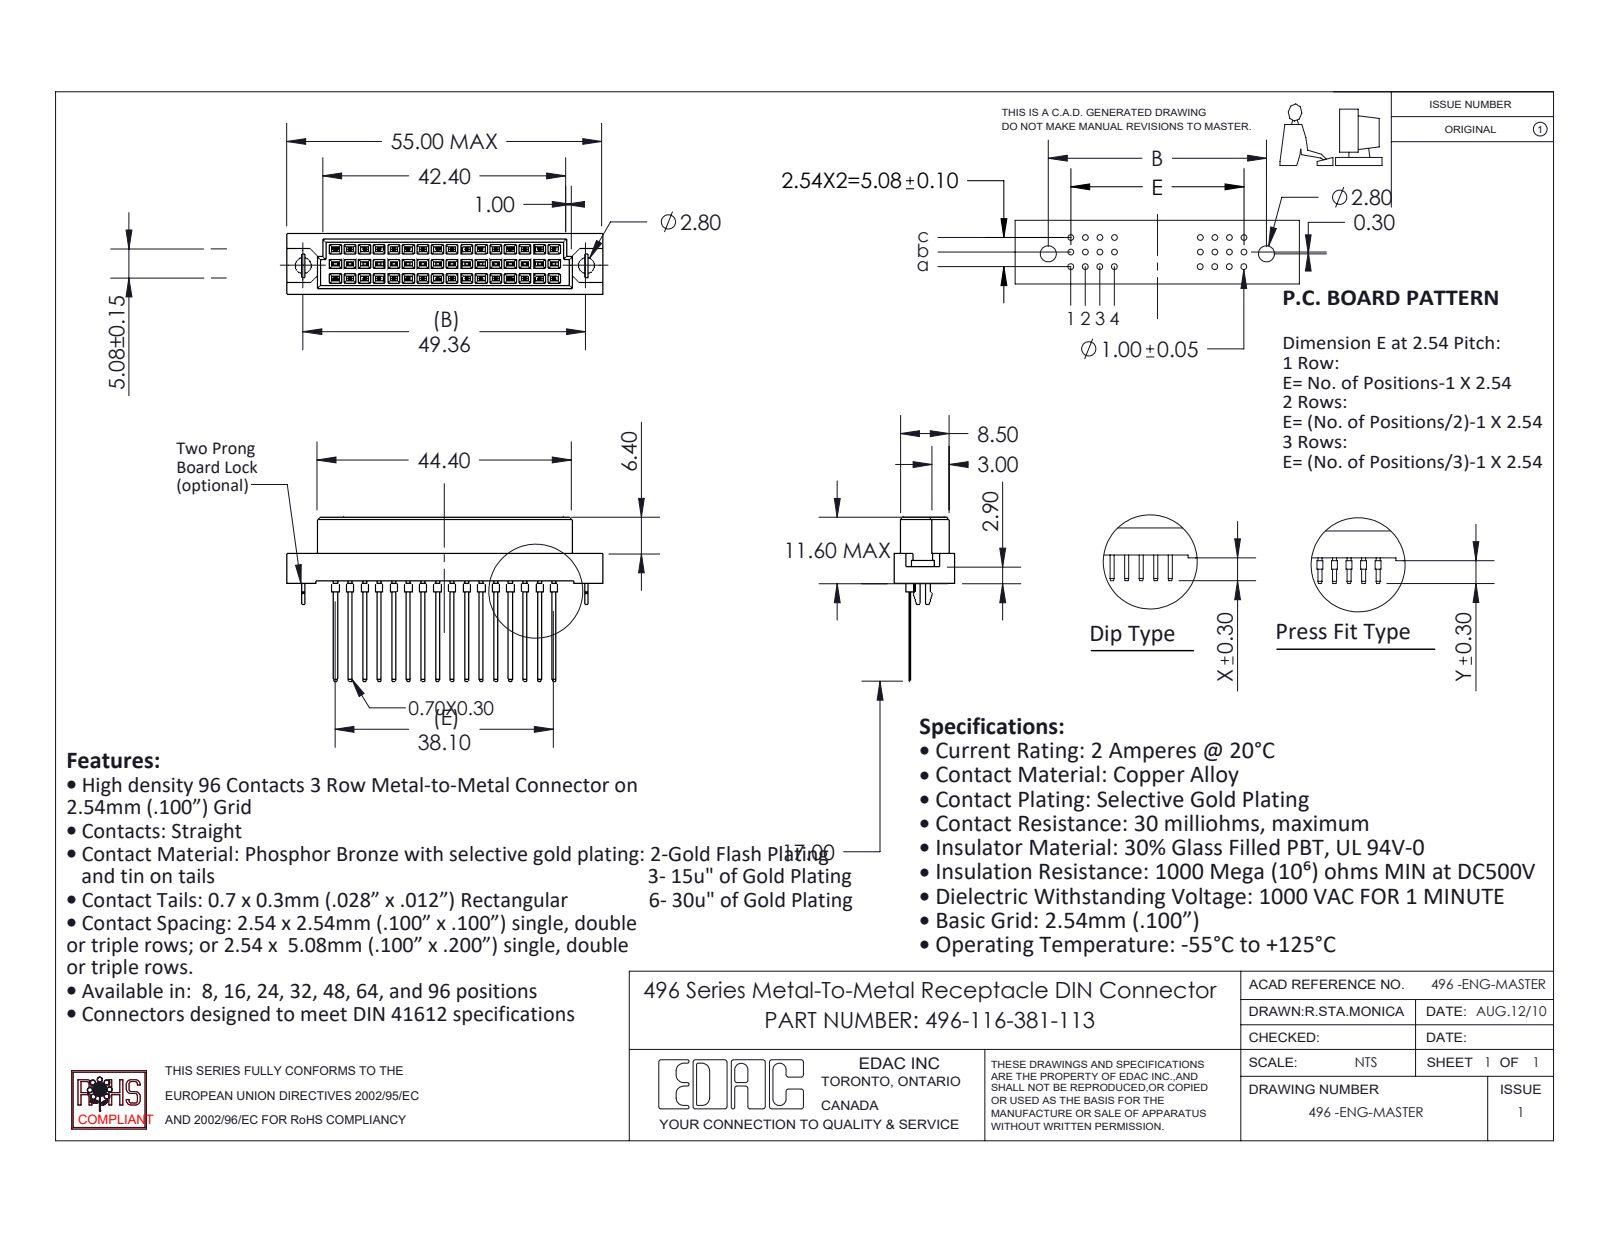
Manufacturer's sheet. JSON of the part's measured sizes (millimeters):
{"part_name": "496 Bore-lock; 496-116-381-113; 496-290_81; 496 Part_48", "step_written_by": "SolidWorks 2020 (CONFIG_CONTROL_DESIGN)", "units": "millimeters", "bodies": {"solids": 19, "faces": 990, "planar": 952, "cylindrical": 38, "other": 0}, "overall_size": [55, 28.6, 10.6], "volume_mm3": 4698, "surface_area_mm2": 5063, "round_holes": [[2.8, 2]], "round_bosses_or_shafts": [[1, 16]], "partial_cylinders_radius": [[0.53, 1]], "face_to_face_distances": [2.54, 1.05, 9.55, 5.08, 0.81, 1.86, 1.56, 2.91, 7.69, 2.61], "hole_center_spacings": [49.36]}
